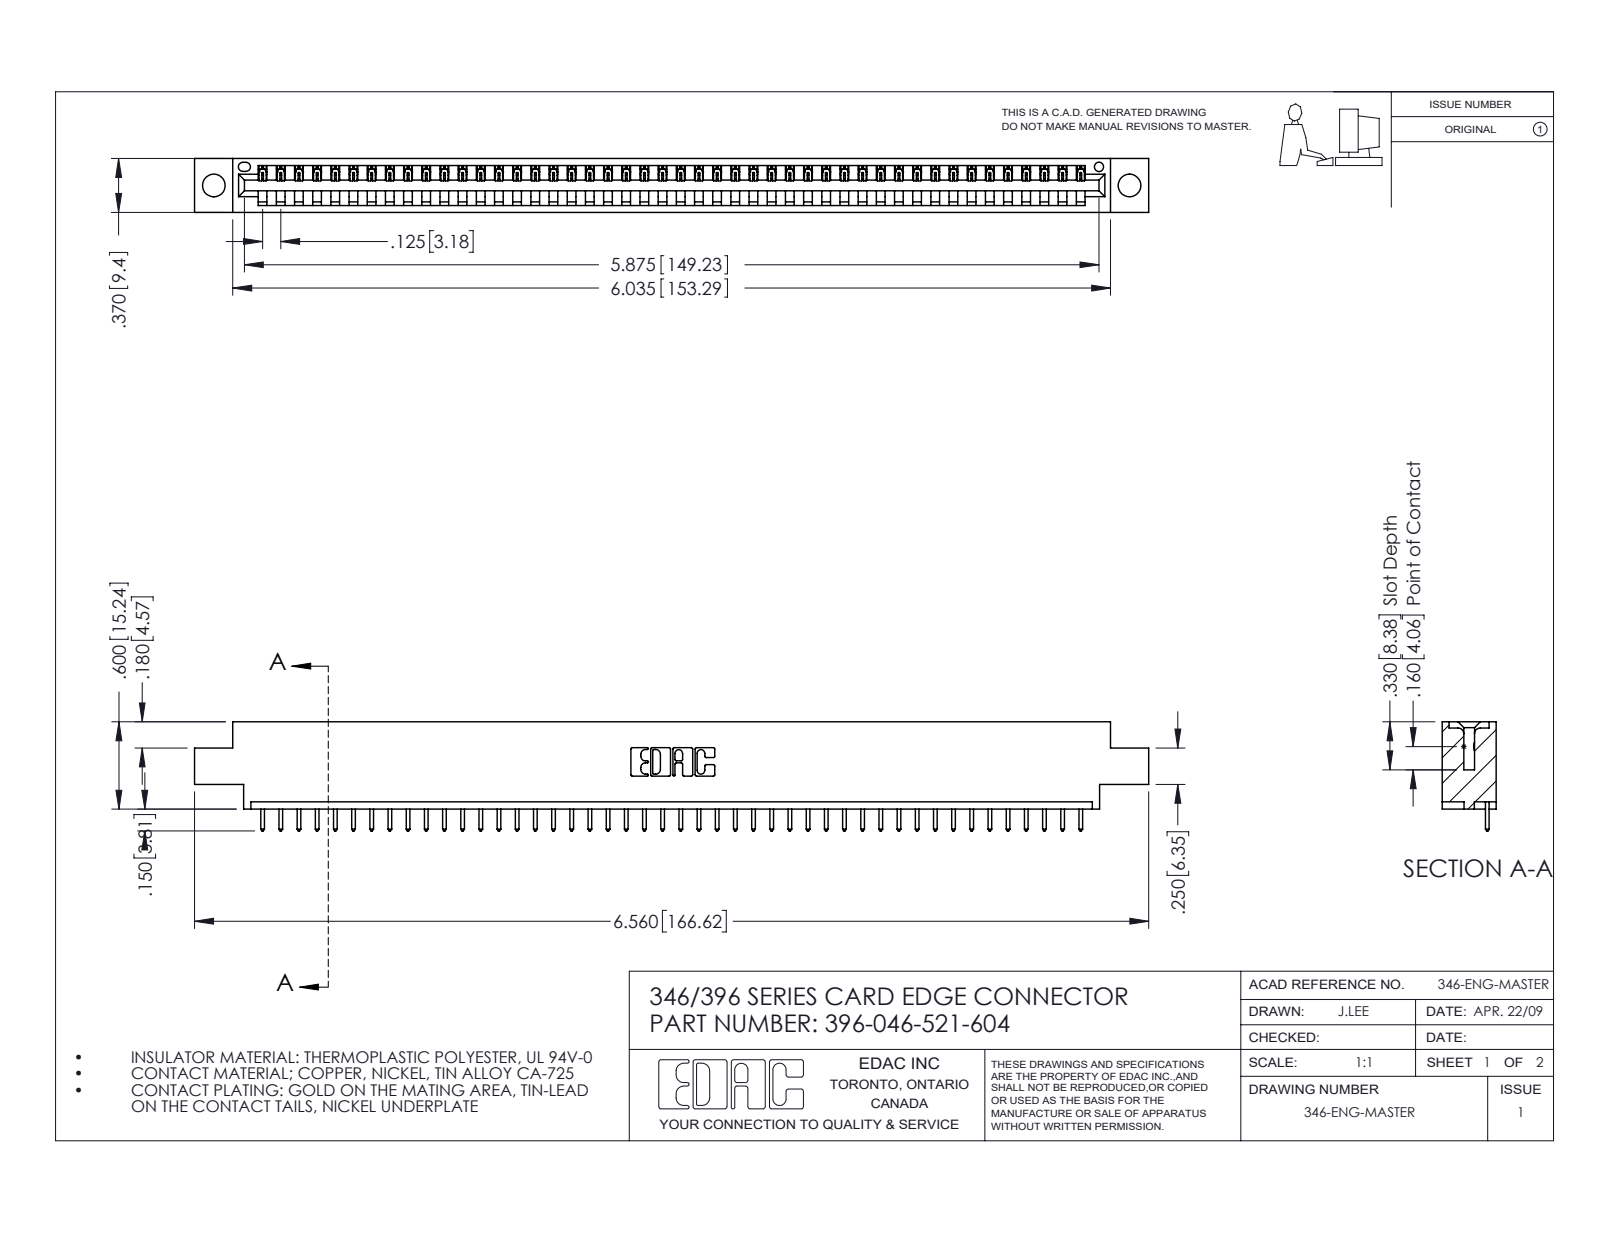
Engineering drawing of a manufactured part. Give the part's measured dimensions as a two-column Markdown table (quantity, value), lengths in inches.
| quantity | value |
| --- | --- |
| part name | 346 Part_0.170 Offset - 0.156 Dia-TH; 396-046-521-604; 345-292-001_345-293-121 |
| STEP written by | SolidWorks 2016 (CONFIG_CONTROL_DESIGN) |
| units | inches |
| bodies | 47 solids, 2794 faces (1920 planar, 874 cylindrical, 0 other) |
| overall size | 6.56 × 0.75 × 0.37 |
| volume | 0.952 in³ |
| surface area | 29.44 in² |
| round holes (diameter × count) | 0.156 × 2, 0.064 × 1 |
| partial cylindrical surfaces (radius × count) | 0.006 × 92, 0.01 × 92, 0.01 × 22, 0.007 × 6, 0.031 × 6, 0.026 × 3, 0.031 × 2, 0.04 × 2 |
| main face-to-face distances | 0.048, 0.322, 0.37, 0.25, 0.072, 0.298, 0.025, 0.148, 0.222, 0.1 |
| hole center spacings | 0.246, 6.086, 6.295 |
